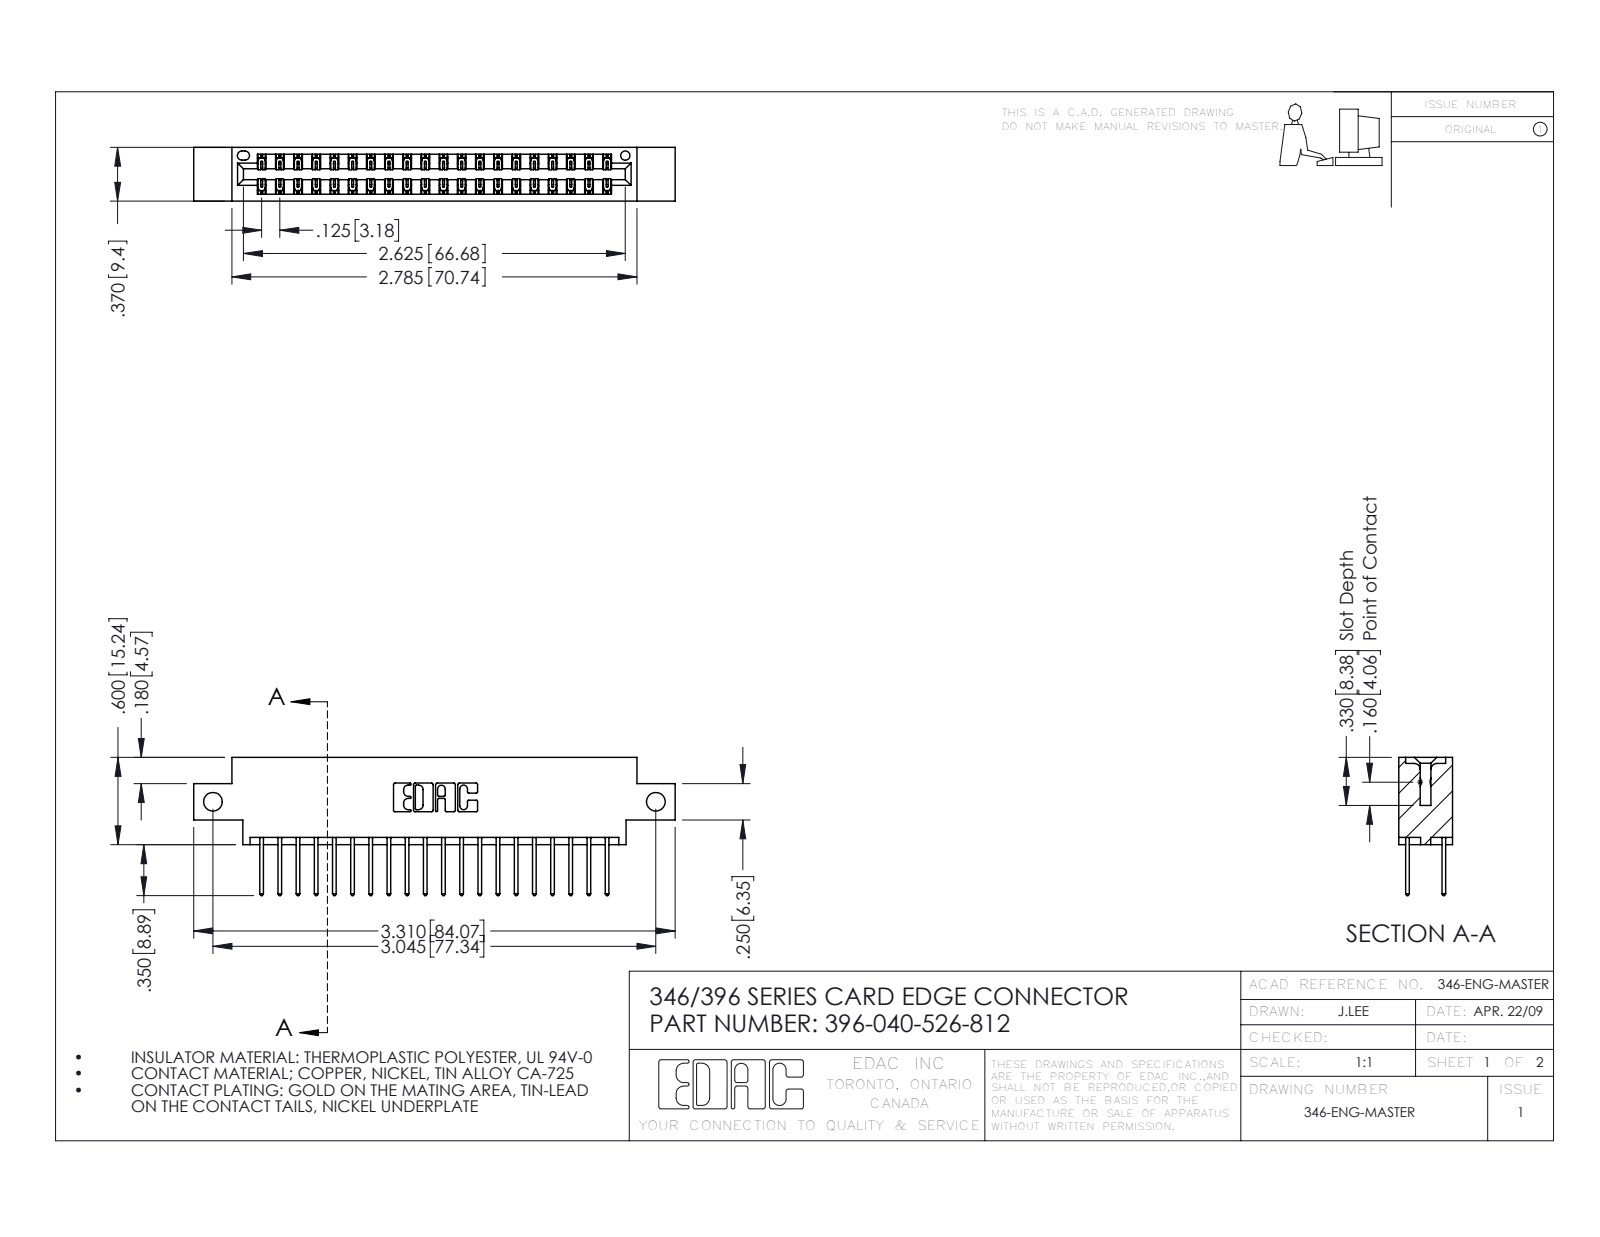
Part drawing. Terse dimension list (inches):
name: 396-040-526-812; 345-292-001_345-293-126; 346 Part_0.170 Offset - Side Mount
written by: SolidWorks 2016 (CONFIG_CONTROL_DESIGN)
unit: in
bodies: 41 solids, 2206 faces (1480 planar, 726 cylindrical, 0 other)
size: 3.31 × 0.95 × 0.37
volume: 0.479 in³; area: 16.71 in²
holes: 2× ⌀0.128, 1× ⌀0.064
rounds: 60× R0.006, 40× R0.01, 22× R0.01, 6× R0.007, 6× R0.031, 3× R0.026, 2× R0.014, 2× R0.022
face distances: 0.048, 0.322, 0.25, 0.37, 0.072, 0.298, 0.025, 0.275, 0.148, 0.222
hole spacings: 3.045
